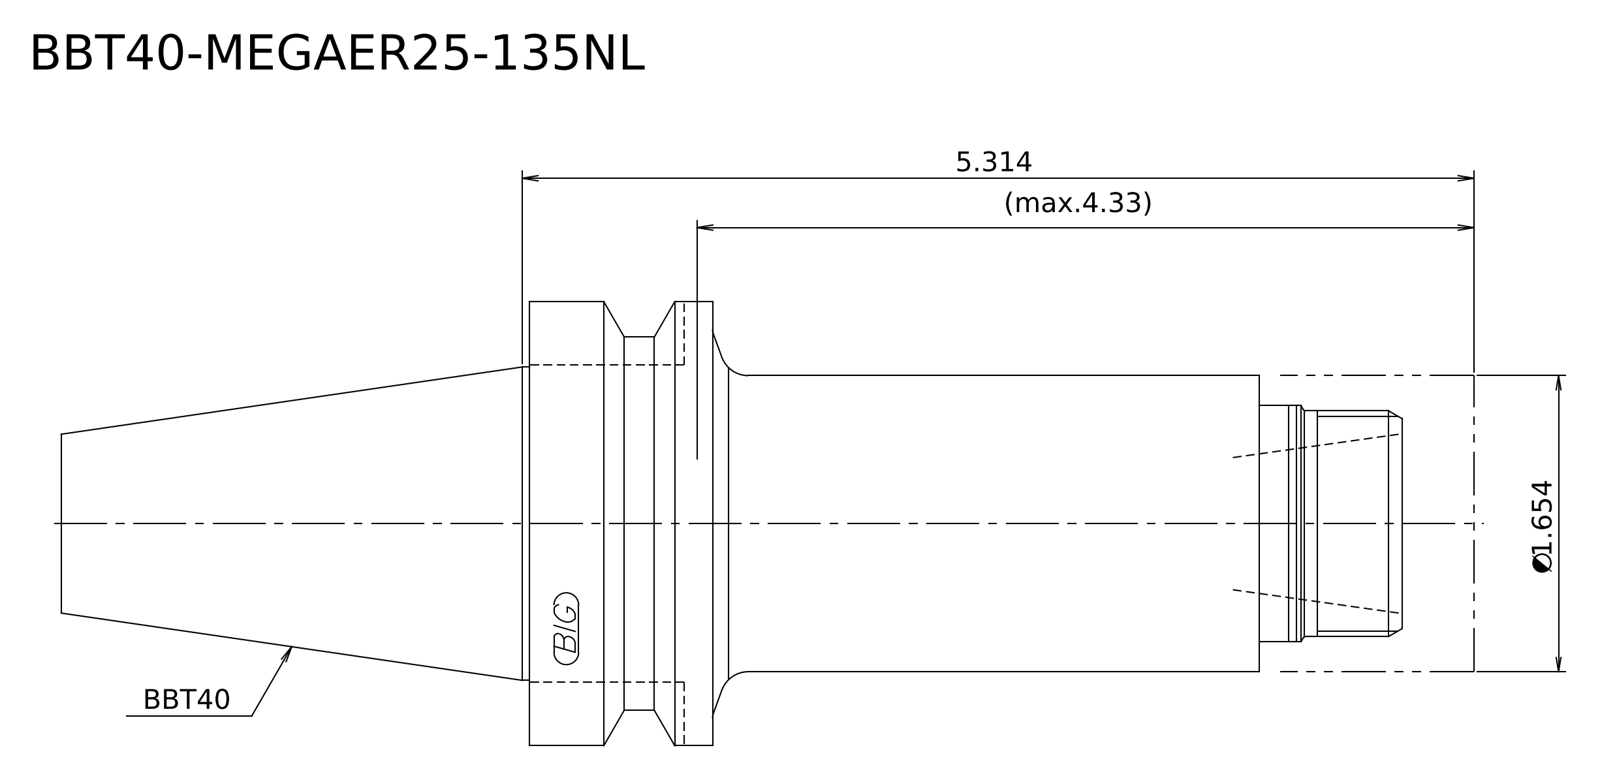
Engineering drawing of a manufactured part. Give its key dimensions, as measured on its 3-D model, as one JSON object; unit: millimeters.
{"step_written_by": "Kubotek KeyCreator 2011 V10.0.2 (22737) (automotive_design)", "units": "millimeters", "bodies": {"solids": 2, "faces": 21, "planar": 7, "cylindrical": 8, "other": 6}, "overall_size": [200.4, 63, 63], "volume_mm3": 304743, "surface_area_mm2": 36722, "round_bosses_or_shafts": [[63, 1], [53, 1], [44.45, 1], [42, 1], [33.5, 1], [32, 1]], "face_to_face_distances": [106.5, 27.5, 134, 108, 80.5, 26, 10.2, 17.3, 97.8, 123.8]}
